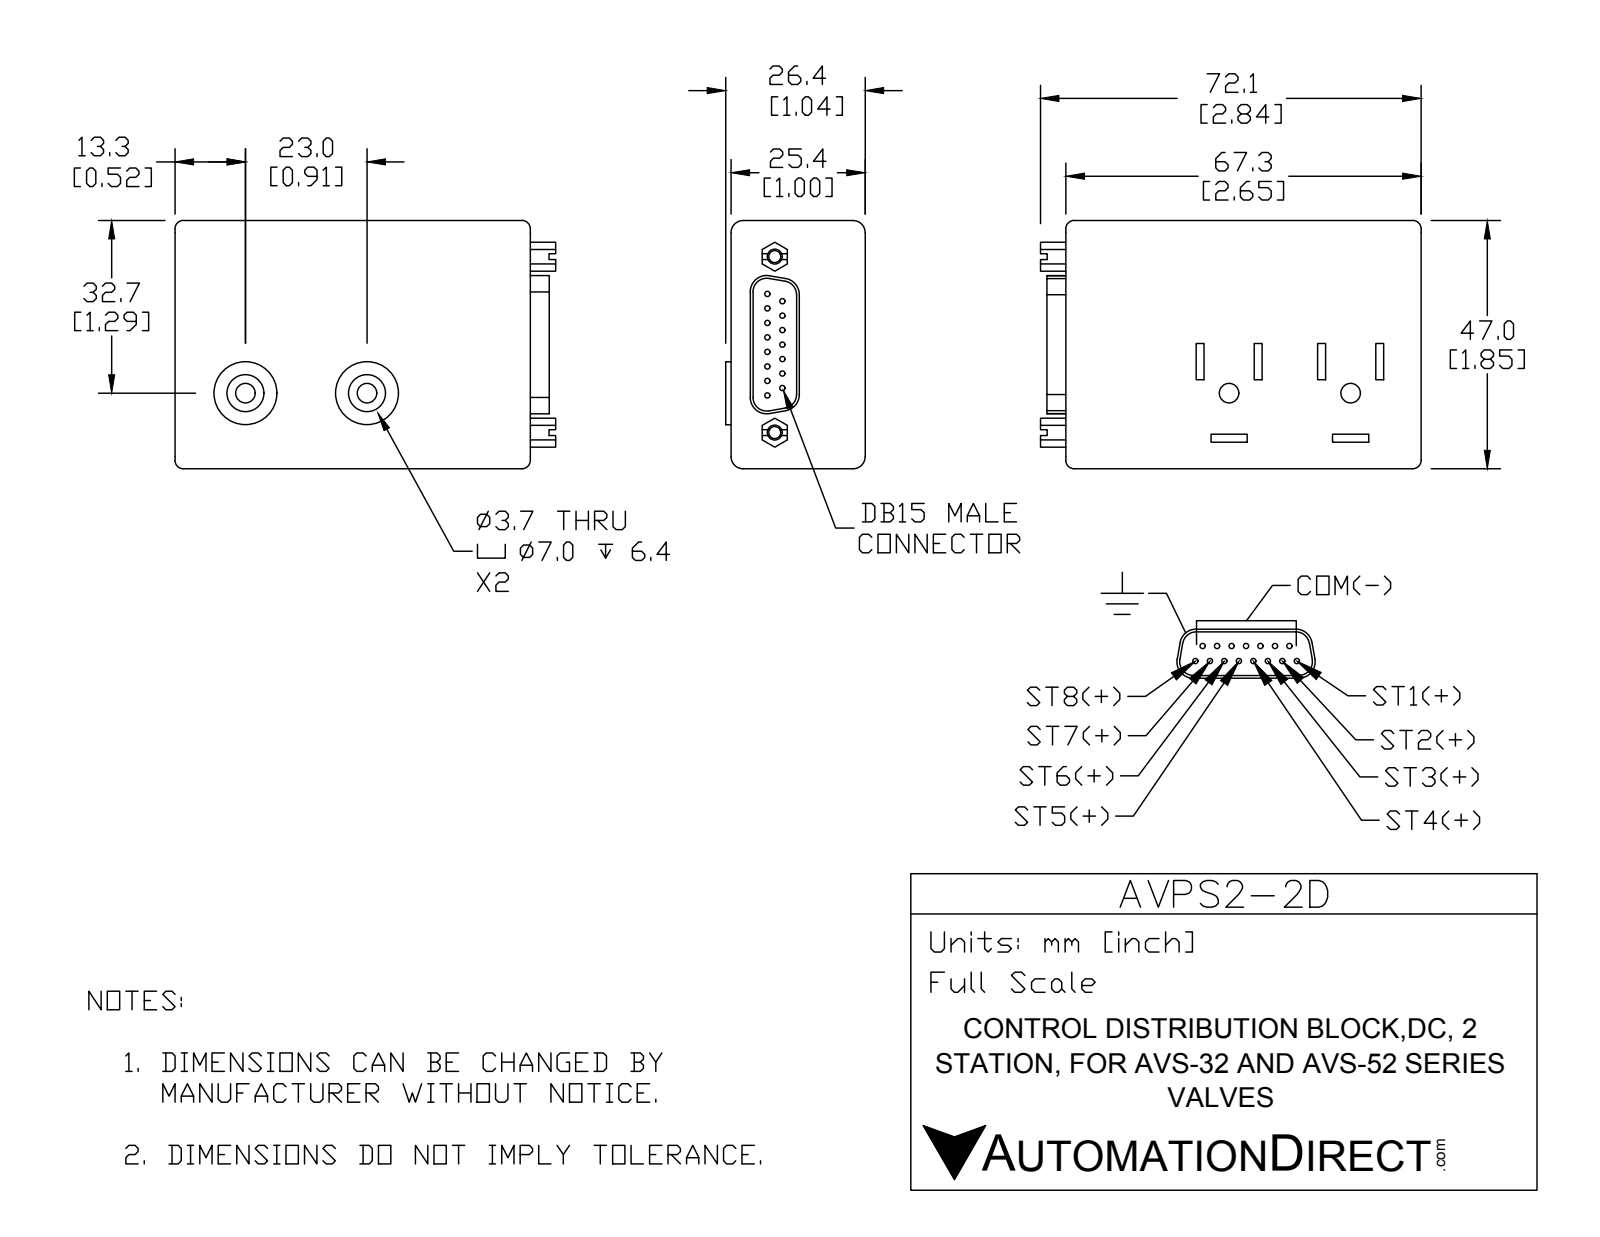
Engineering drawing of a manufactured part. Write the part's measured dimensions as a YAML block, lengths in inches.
part_name: "AVPS2-2D"
step_written_by: "SolidWorks 2016 (AUTOMOTIVE_DESIGN)"
units: inches
bodies: {solids: 1, faces: 173, planar: 93, cylindrical: 68, other: 12}
overall_size: [2.837, 1.85, 1.04]
volume: 4.788
surface_area: 22.01
round_holes:
  - {diameter: 0.089, count: 2}
  - {diameter: 0.145, count: 2}
  - {diameter: 0.275, count: 2}
round_bosses_or_shafts:
  - {diameter: 0.039, count: 15}
  - {diameter: 0.469, count: 2}
partial_cylinders:
  - {radius: 0.062, count: 6}
  - {radius: 0.09, count: 4}
  - {radius: 0.102, count: 4}
  - {radius: 0.122, count: 4}
  - {radius: 0.063, count: 2}
face_to_face_distances: [1, 1.85, 2.648, 0.059, 0.123, 2.525, 0.906, 0.433, 0.02, 0.04]
hole_center_spacings: [0.906, 1.311]
